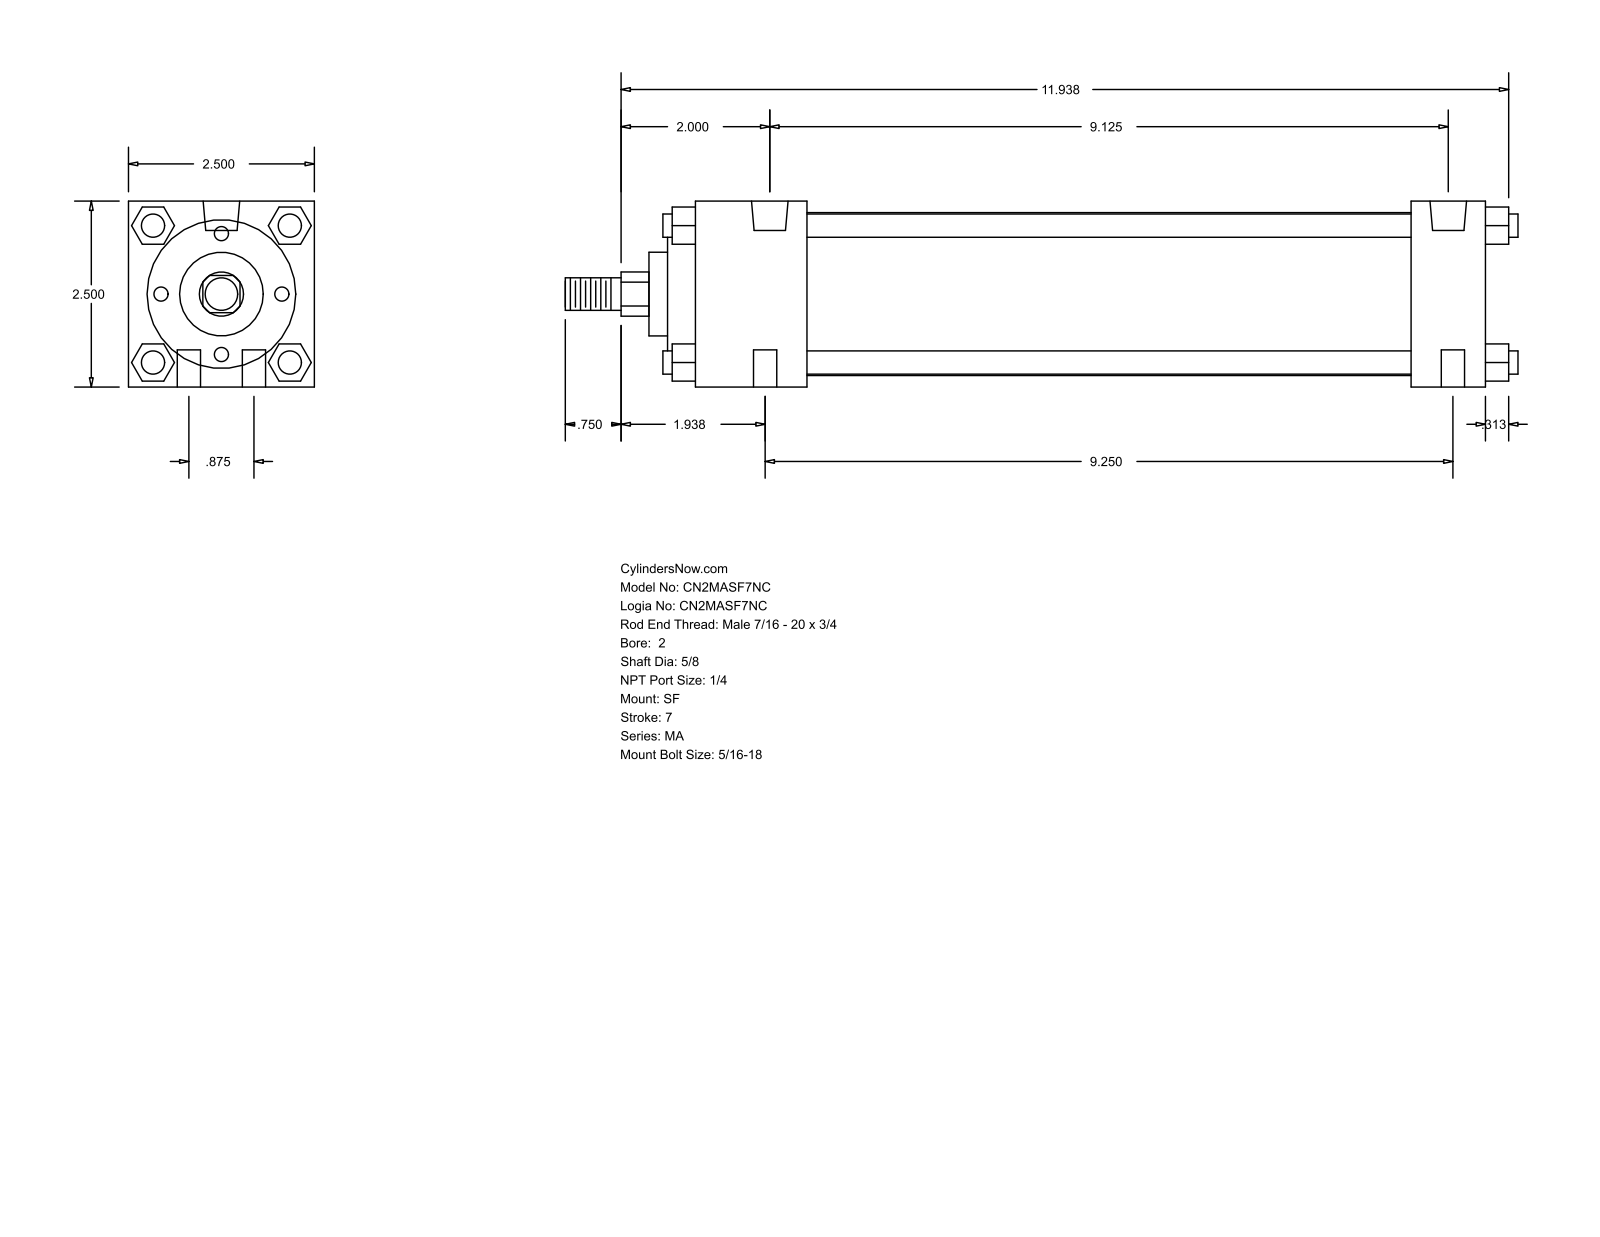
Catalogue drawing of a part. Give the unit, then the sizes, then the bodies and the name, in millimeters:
Units: millimetres
Overall size (bounding box): 325.44 × 63.5 × 63.5
Round holes (diameter × count): ⌀7.94 ×6, ⌀12.49 ×2
Round bosses / shafts (diameter × count): ⌀7.94 ×4, ⌀55.63 ×1, ⌀50.8 ×1, ⌀28.57 ×1, ⌀15.88 ×1, ⌀11.11 ×1
Partial cylindrical surfaces — rounded edges, fillets, slot ends (radius × count): R7.54 ×1
Main face-to-face distances: 63.5, 12.7, 38.1, 269.87, 244.48, 25.39, 206.38, 231.77, 9.52, 47.62
Hole centre spacings: 11.22, 233.62, 22.22, 231.77, 234.95, 236
Bodies: 0 solids, 126 faces (95 planar, 31 cylindrical, 0 other)
Part name (STEP PRODUCT): MA_SF__0200_0.625
STEP written by: GSSL Pune (CONFIG_CONTROL_DESIGN)
